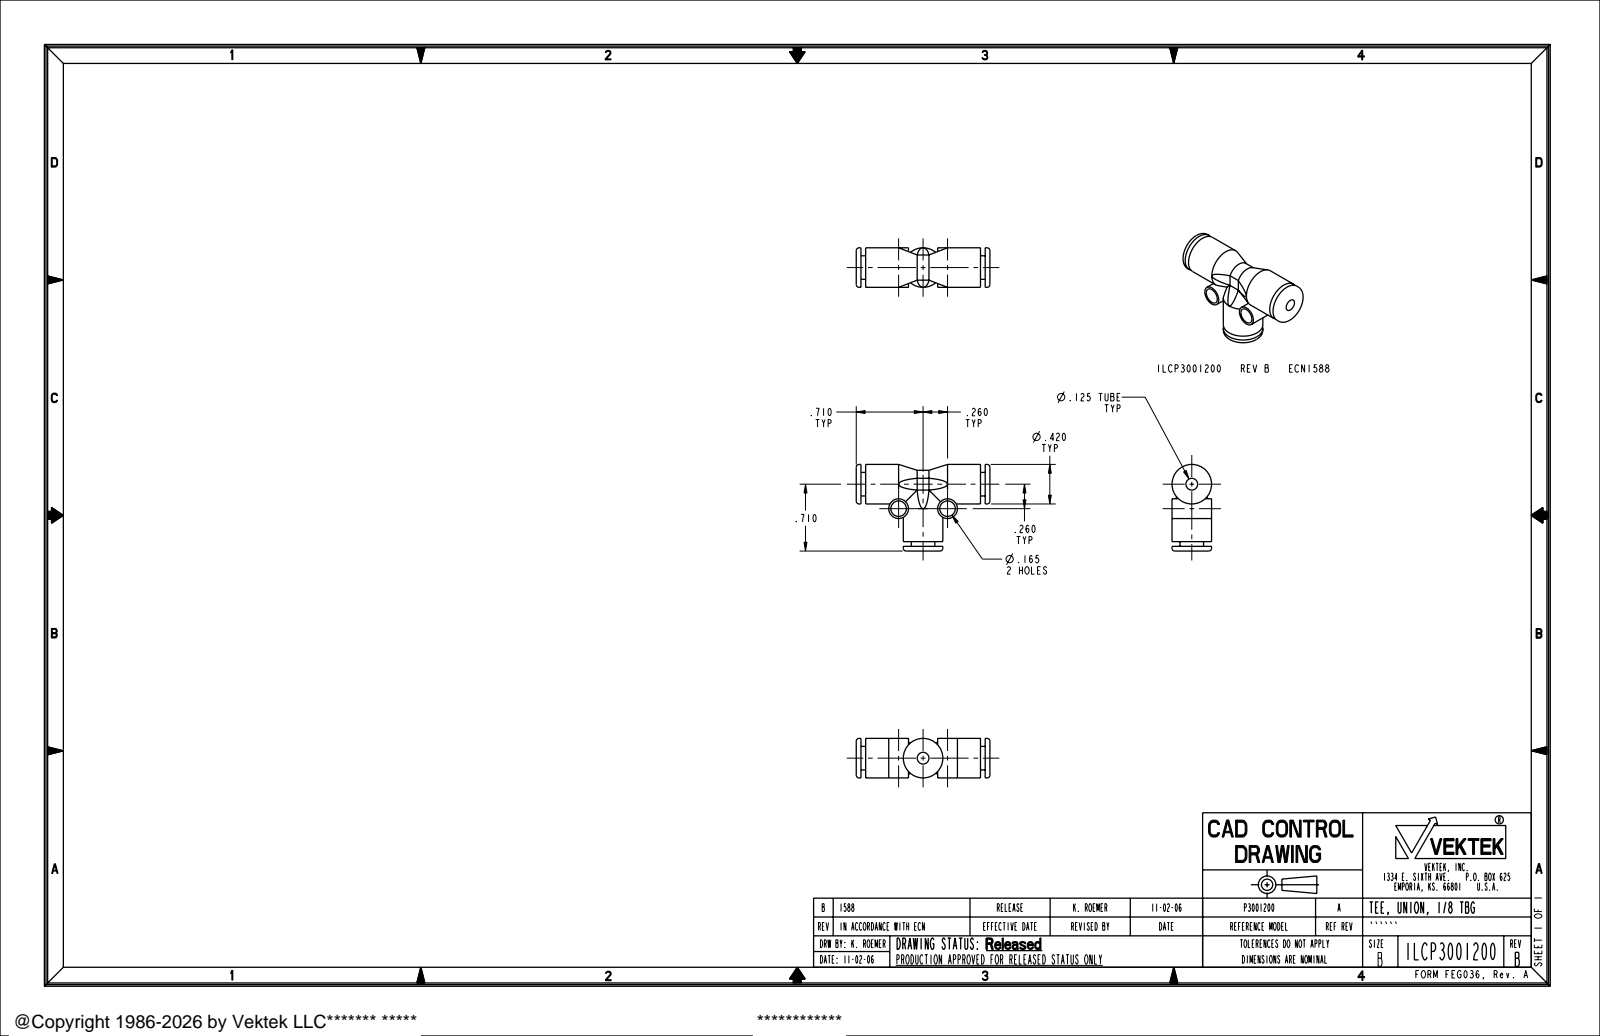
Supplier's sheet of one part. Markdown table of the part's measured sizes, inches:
| quantity | value |
| --- | --- |
| part name | ILCP3001200 |
| STEP written by | PRO/ENGINEER BY PARAMETRIC TECHNOLOGY CORPORATION, 2005180 (AUTOMOTIVE_DESIGN_CC2) |
| units | inches |
| bodies | 1 solid, 68 faces (21 planar, 31 cylindrical, 16 other) |
| overall size | 1.42 × 0.92 × 0.42 |
| volume | 0.217 in³ |
| surface area | 4.732 in² |
| round holes (diameter × count) | 0.125 × 2, 0.165 × 1, 0.165 × 1 |
| round bosses / shafts (diameter × count) | 0.42 × 2, 0.25 × 2, 0.21 × 2 |
| partial cylindrical surfaces (radius × count) | 0.147 × 1 |
| main face-to-face distances | 0.05, 0.1, 1.32, 1.37, 1.27, 1.42, 1.22, 0.204, 0.076, 0.343 |
| hole center spacings | 0.52 |
